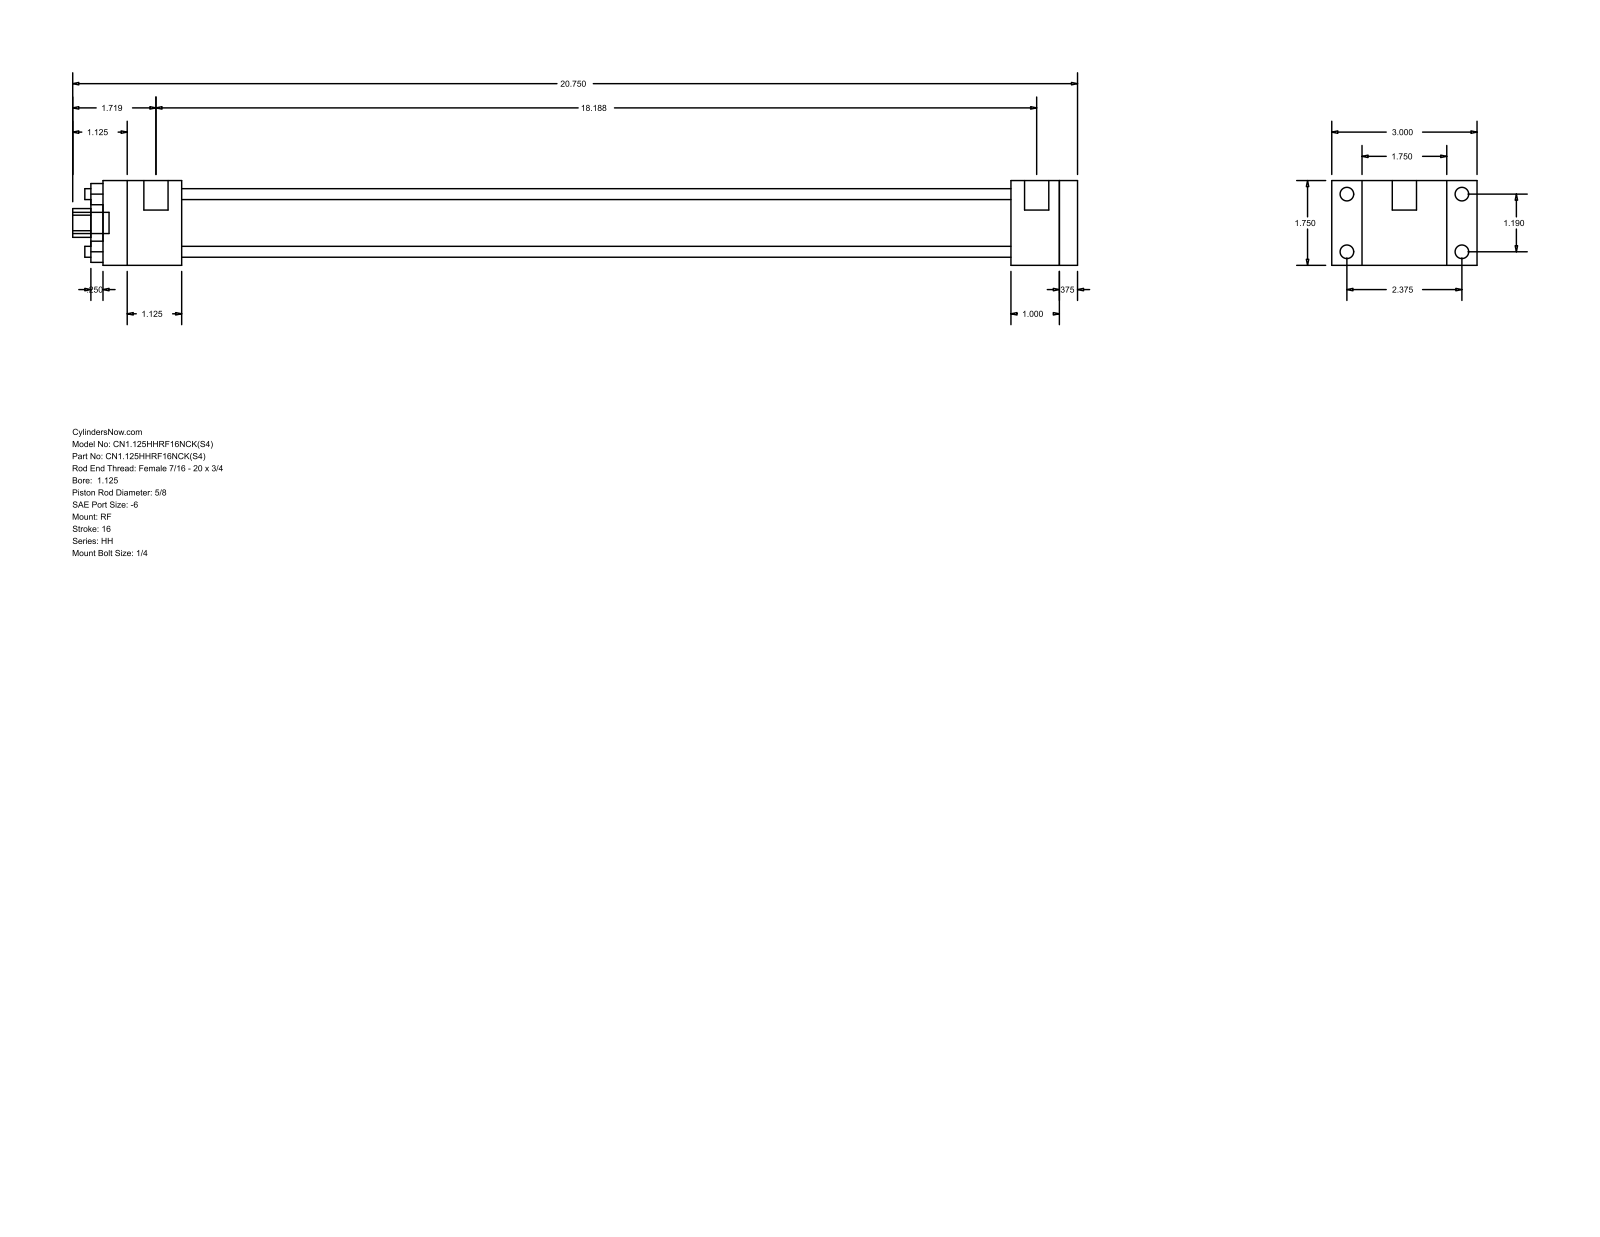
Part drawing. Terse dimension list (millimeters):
name: HH_RF__0112_0.625
written by: GSSL Pune (CONFIG_CONTROL_DESIGN)
unit: mm
bodies: 0 solids, 92 faces (64 planar, 28 cylindrical, 0 other)
size: 527.05 × 76.2 × 44.45
holes: 4× ⌀5.71, 1× ⌀15.88, 1× ⌀28.57, 1× ⌀34.92
bosses: 4× ⌀7.14, 4× ⌀5.56, 2× ⌀12.7, 1× ⌀11.11
rounds: 1× R7.54
face distances: 44.46, 9.53, 511.17, 15.87, 460.37, 469.9, 434.97, 25.4, 34.93, 41.27
hole spacings: 21.37, 30.22, 42.74
